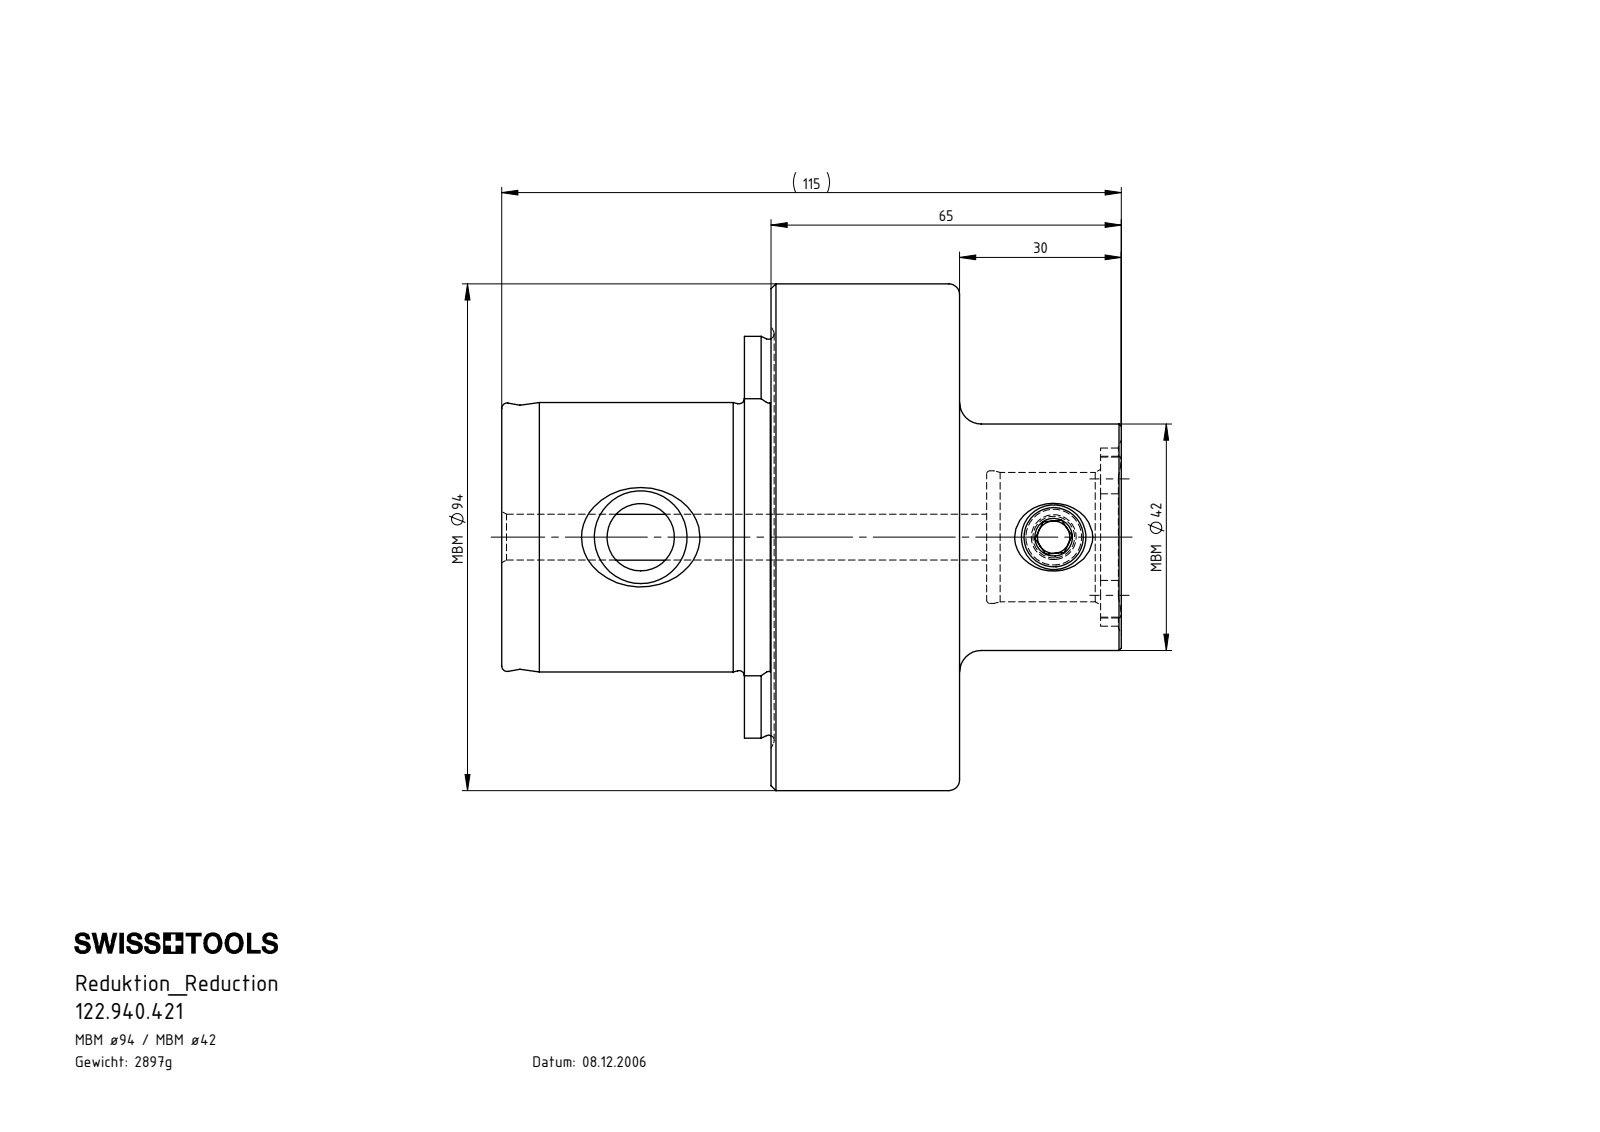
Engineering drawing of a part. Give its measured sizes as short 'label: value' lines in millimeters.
name: 122.940.421; MB9-MB4.K01.065_C; MB4-ER1.001.013_A
written by: SolidWorks 2017 (CONFIG_CONTROL_DESIGN)
unit: mm
bodies: 2 solids, 135 faces (35 planar, 35 cylindrical, 65 other)
size: 115 × 94 × 94
volume: 369 075 mm³; area: 41 387 mm²
holes: 1× ⌀6, 1× ⌀8.5, 1× ⌀11, 1× ⌀12.5, 1× ⌀24, 1× ⌀24.6
bosses: 1× ⌀94, 1× ⌀50, 1× ⌀42, 1× ⌀12
rounds: 4× R4.2, 1× R14.9, 1× R16.52, 1× R37.27
face distances: 35, 50, 85, 45.05, 4.95, 39.95, 49.85, 4.8, 35.15, 90
hole spacings: 76.65
